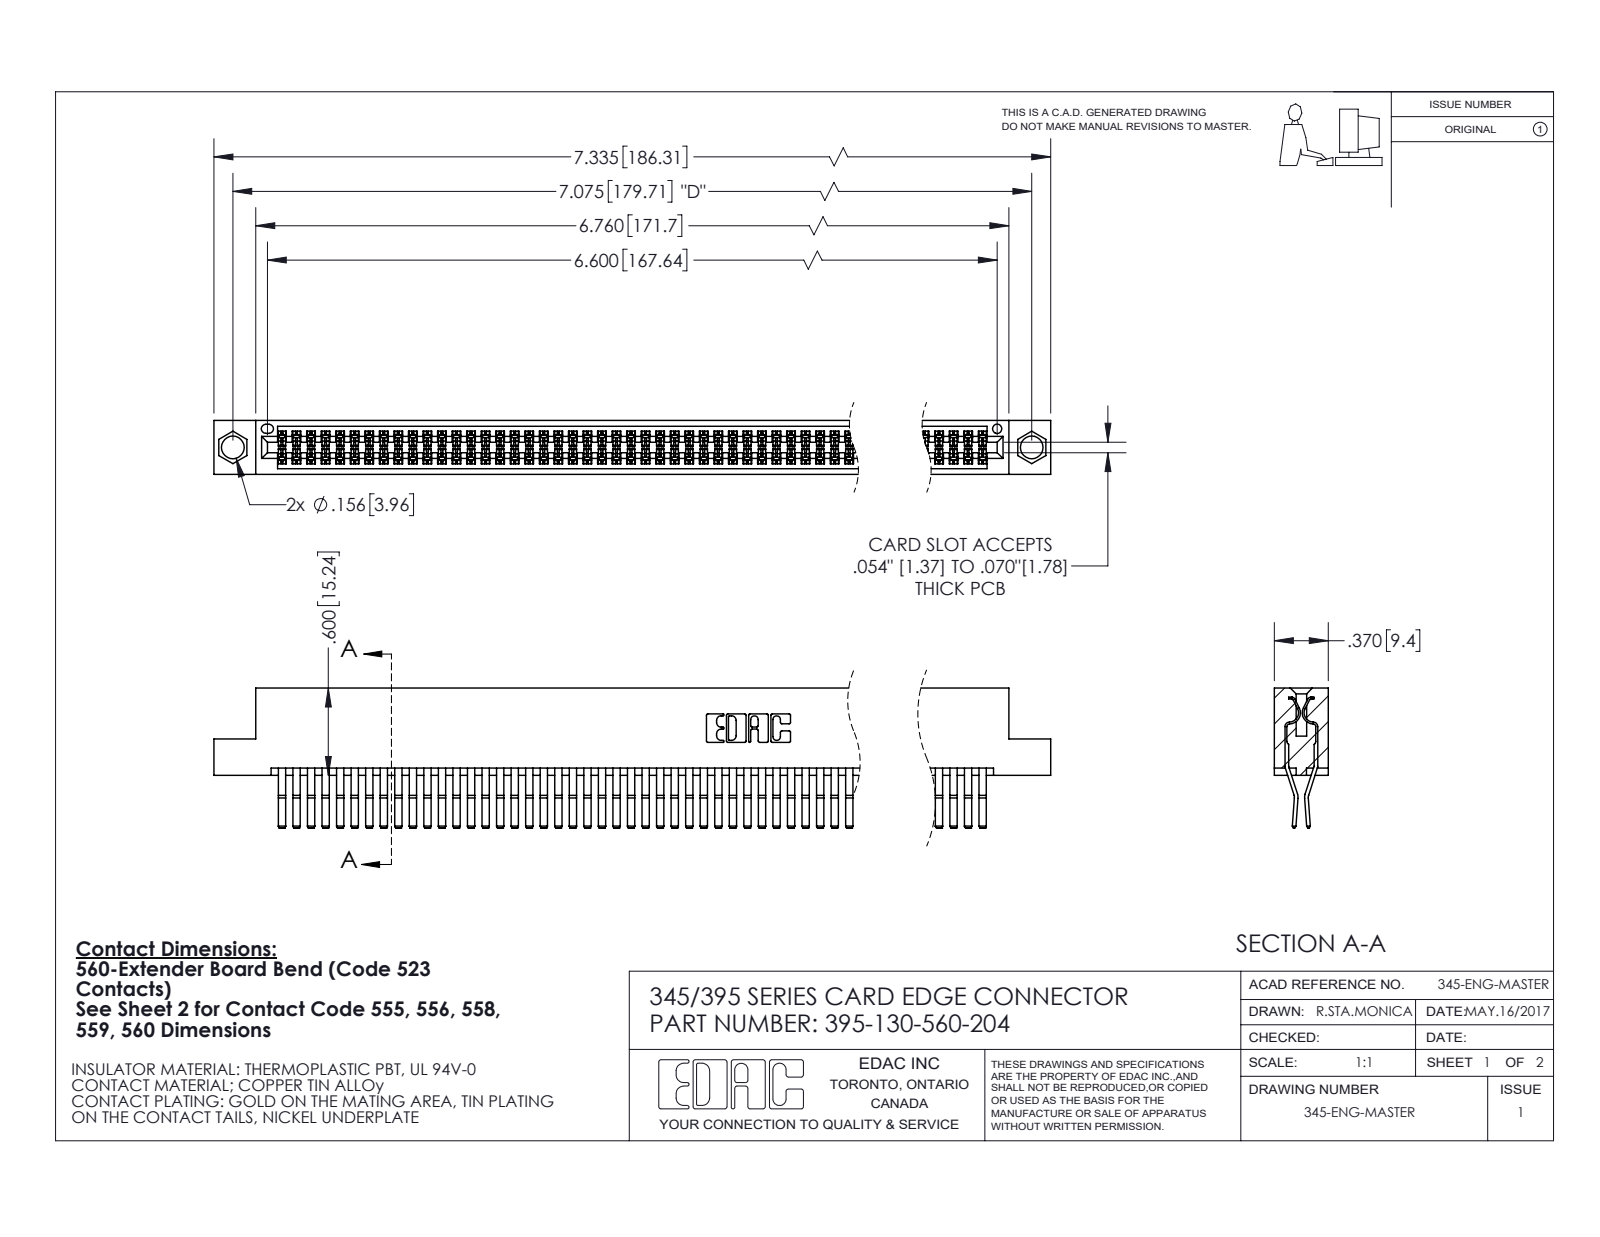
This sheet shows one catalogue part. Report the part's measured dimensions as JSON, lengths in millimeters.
{"part_name": "345-292-001_560 Tail; 395-130-560-204; 345 Part_Flush Mounting Lugs - 0.156 Dia-TI", "step_written_by": "SolidWorks 2020 (CONFIG_CONTROL_DESIGN)", "units": "millimeters", "bodies": {"solids": 131, "faces": 6900, "planar": 4384, "cylindrical": 2516, "other": 0}, "overall_size": [186.3, 24.4, 9.4], "volume_mm3": 19060, "surface_area_mm2": 30660, "round_holes": [[4, 2], [1.6, 1]], "partial_cylinders_radius": [[0.2, 195], [0.3, 22], [0.2, 6], [0.8, 6], [0.7, 3], [0.3, 2], [0.4, 2], [0.5, 2]], "face_to_face_distances": [0.6, 7.6, 1.8, 9.4, 5.1, 2.5, 6.9, 5.7, 4.4, 3.8], "hole_center_spacings": [6.9, 173.7, 179.7]}
